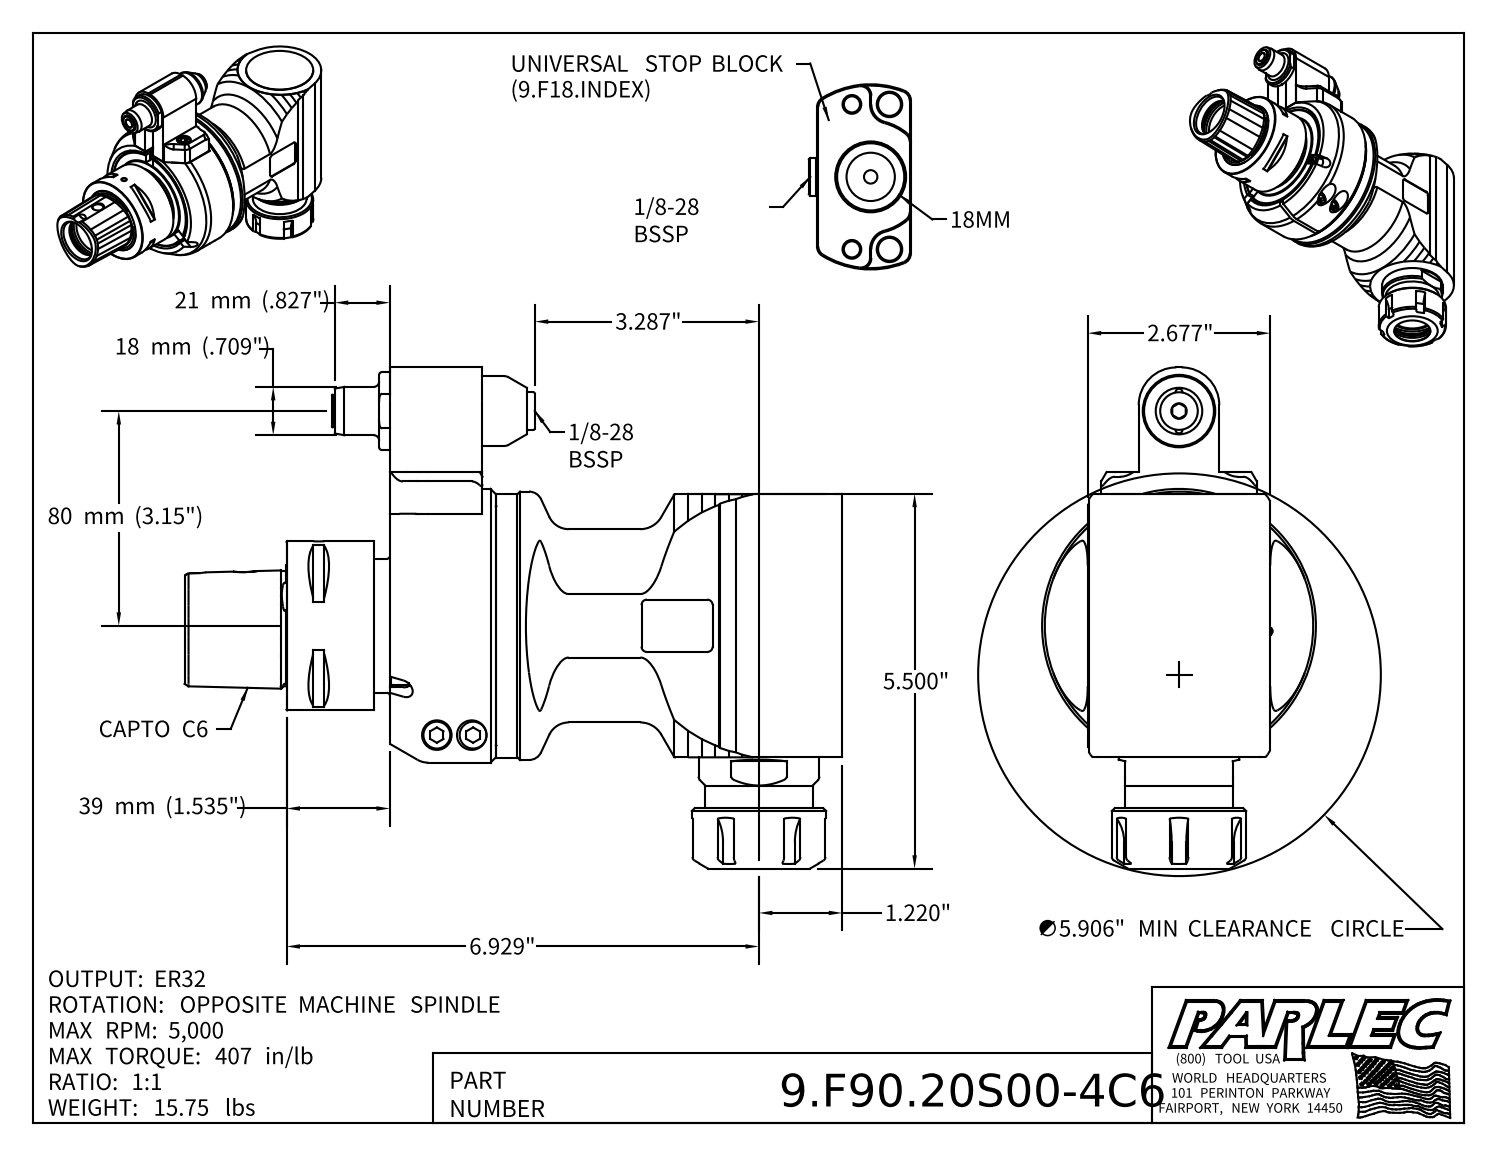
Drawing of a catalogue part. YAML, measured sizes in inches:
part_name: "9.F90.20S00-4C6; 9_F90_20S00; 9_GA1_668_2 (EVO, Type 1, Capto C6, 80mm)"
step_written_by: "Autodesk Inventor 2022 (AUTOMOTIVE_DESIGN)"
units: inches
bodies: {solids: 8, faces: 566, planar: 260, cylindrical: 112, other: 194}
overall_size: [9.646, 7.352, 4.016]
volume: 74.56
surface_area: 259
round_holes:
  - {diameter: 0.492, count: 3}
  - {diameter: 0.102, count: 2}
  - {diameter: 0.165, count: 2}
  - {diameter: 0.197, count: 2}
  - {diameter: 0.409, count: 2}
  - {diameter: 0.433, count: 2}
  - {diameter: 1.063, count: 2}
  - {diameter: 0.098, count: 1}
  - {diameter: 0.118, count: 1}
  - {diameter: 0.157, count: 1}
  - {diameter: 0.256, count: 1}
  - {diameter: 0.276, count: 1}
round_bosses_or_shafts:
  - {diameter: 0.394, count: 4}
  - {diameter: 0.236, count: 4}
  - {diameter: 1.969, count: 2}
  - {diameter: 0.098, count: 2}
  - {diameter: 4.016, count: 1}
  - {diameter: 3.937, count: 1}
  - {diameter: 3.874, count: 1}
  - {diameter: 3.031, count: 1}
partial_cylinders:
  - {radius: 0.079, count: 12}
  - {radius: 0.591, count: 6}
  - {radius: 0.157, count: 4}
  - {radius: 0.197, count: 3}
  - {radius: 0.02, count: 2}
  - {radius: 0.039, count: 2}
  - {radius: 0.138, count: 2}
  - {radius: 0.551, count: 2}
face_to_face_distances: [1.26, 0.02, 1.28, 0.748, 0.285, 0.256, 0.531, 1.555, 0.276, 1.791]
hole_center_spacings: [0.276, 0.512, 0.551, 1.083, 1.72, 1.849, 2.281, 2.858]
